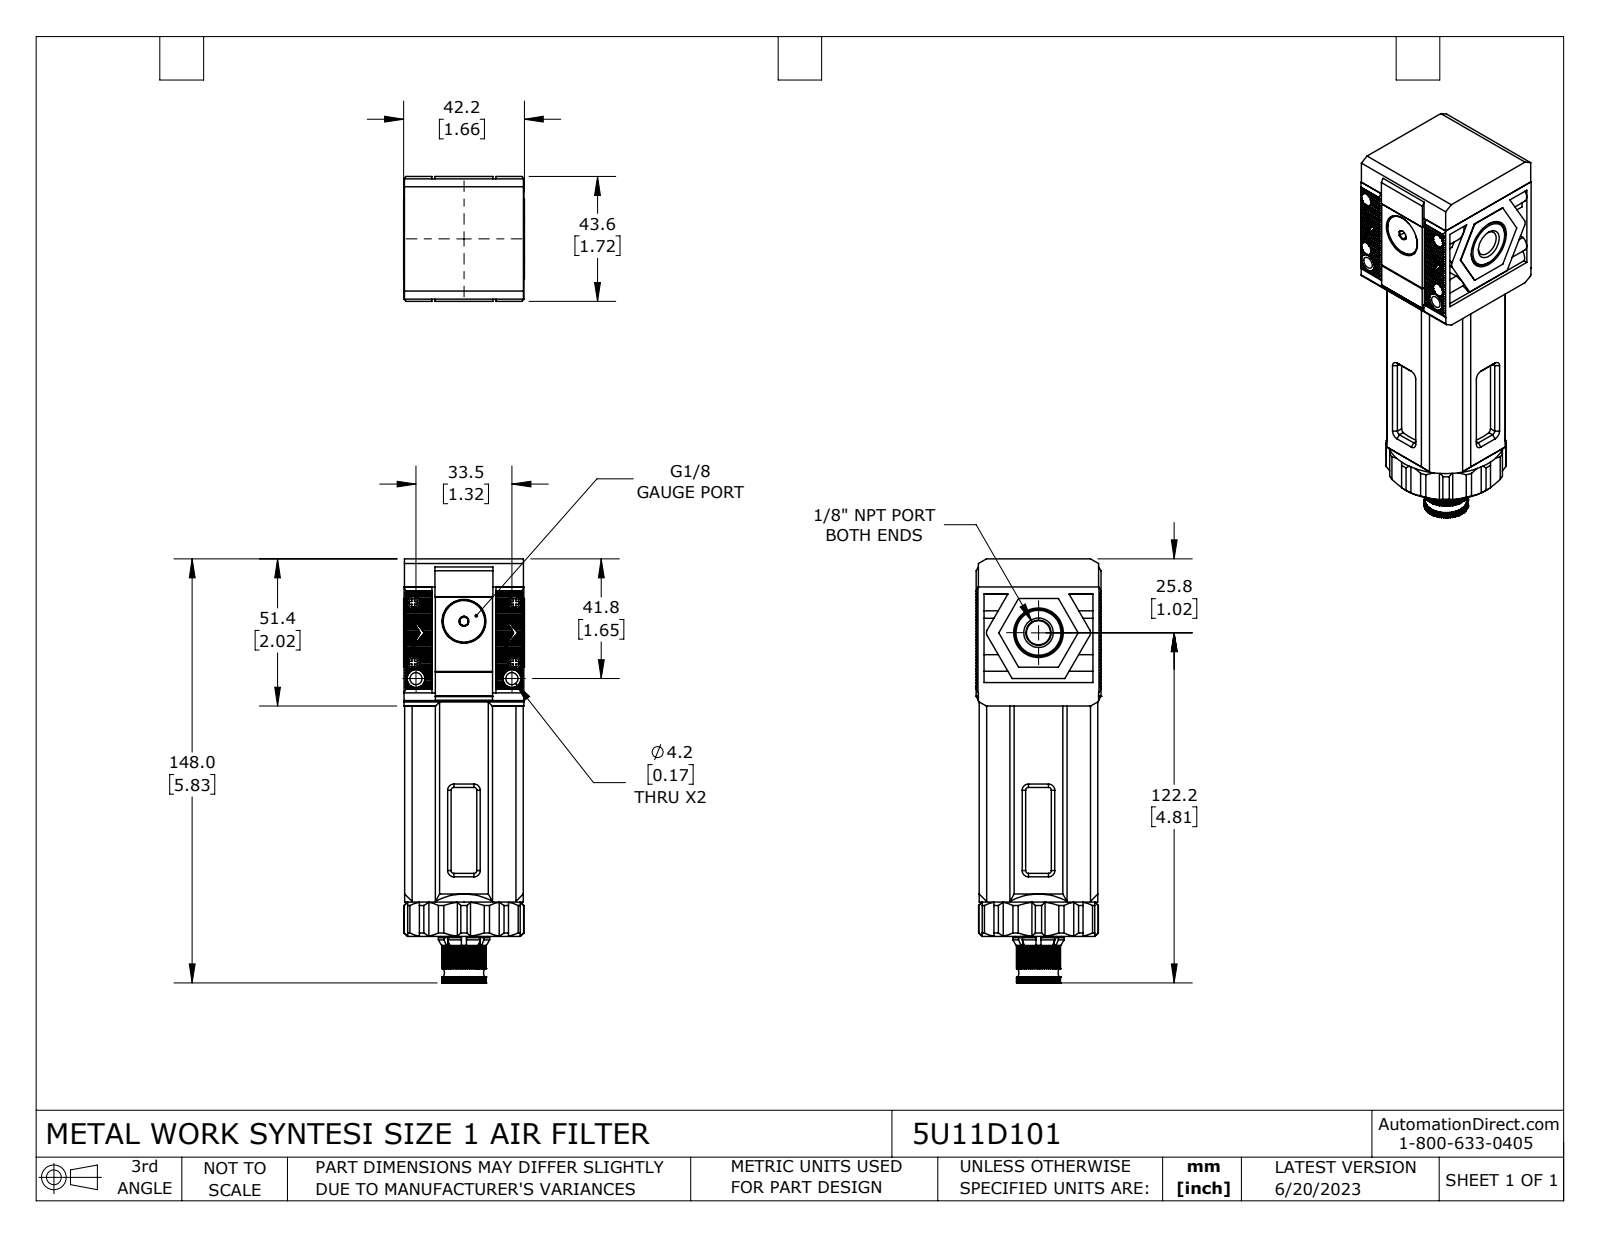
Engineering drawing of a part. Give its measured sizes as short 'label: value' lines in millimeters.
name: 5U11D101
written by: SolidWorks 2021 (CONFIG_CONTROL_DESIGN)
unit: mm
bodies: 14 solids, 1872 faces (1424 planar, 286 cylindrical, 162 other)
size: 148 × 43.6 × 42.2
volume: 131 500 mm³; area: 65 420 mm²
holes: 4× ⌀2.1, 4× ⌀3, 4× ⌀4.7, 2× ⌀4.2, 1× ⌀3.2, 1× ⌀7, 1× ⌀8.6, 1× ⌀8.7, 1× ⌀15.3, 1× ⌀30, 1× ⌀34, 1× ⌀35.4
bosses: 4× ⌀4.6, 4× ⌀2.6, 2× ⌀6.2, 1× ⌀41.4, 1× ⌀35.6, 1× ⌀25, 1× ⌀22.8, 1× ⌀18.2
rounds: 8× R1, 4× R0.6, 4× R3.1, 2× R0.2, 2× R2, 1× R7, 1× R7.1, 1× R9
face distances: 41.6, 41.4, 1.1, 42.5, 41.8, 9.8, 33.8, 7.6, 34, 7.8
hole spacings: 5.6, 18.8, 20.9, 22.9, 26.1, 26.5, 34.9, 35.4
